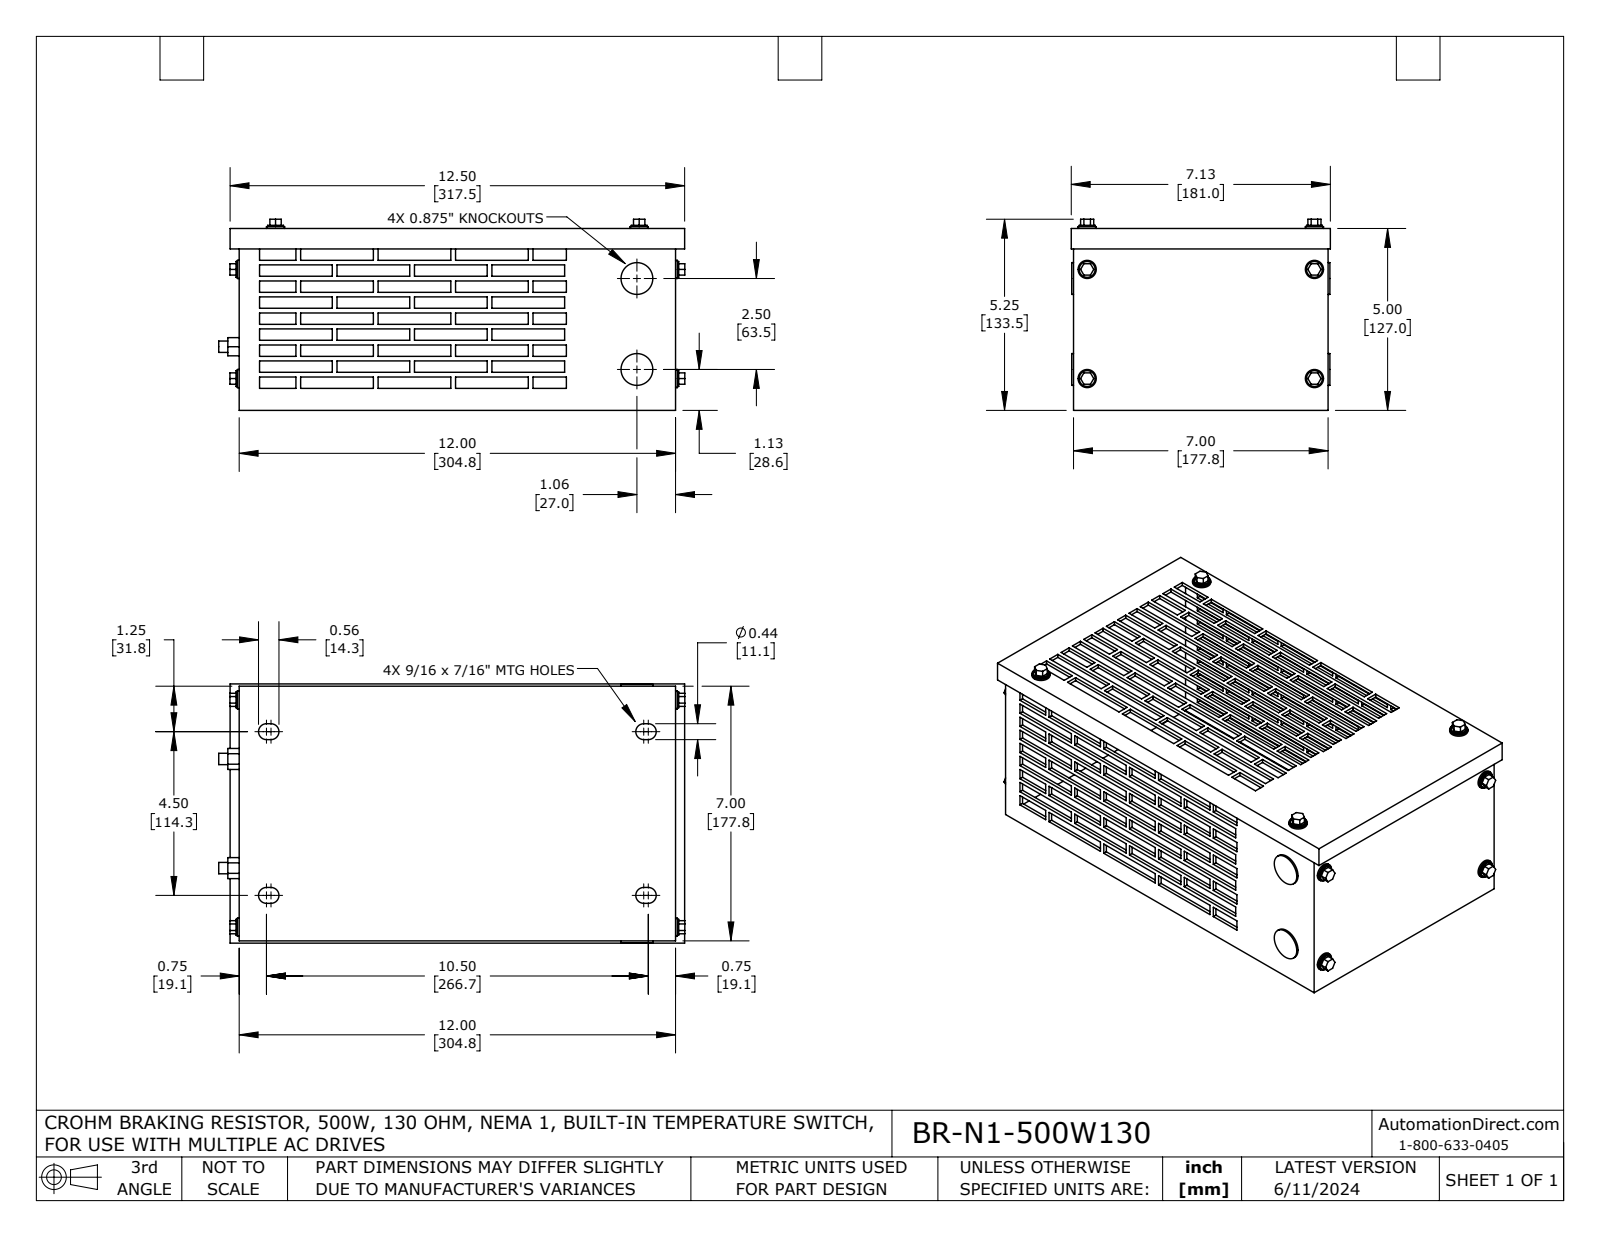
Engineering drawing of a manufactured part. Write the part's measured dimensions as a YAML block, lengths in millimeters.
part_name: "BR-N1-500W130"
step_written_by: "SolidWorks 2021 (AUTOMOTIVE_DESIGN)"
units: millimeters
bodies: {solids: 31, faces: 846, planar: 746, cylindrical: 100, other: 0}
overall_size: [325.6, 181, 133.5]
volume: 468500
surface_area: 412400
round_holes:
  - {diameter: 6.4, count: 8}
  - {diameter: 19.1, count: 2}
round_bosses_or_shafts:
  - {diameter: 12.7, count: 8}
  - {diameter: 11.1, count: 8}
  - {diameter: 22.2, count: 2}
  - {diameter: 8, count: 2}
partial_cylinders:
  - {radius: 5.6, count: 8}
face_to_face_distances: [2.5, 124.5, 302.3, 175.3, 127, 121.9, 304.8, 177.8, 299.7, 172.7]
hole_center_spacings: [158.8, 76.2, 176.1, 254, 299.5, 63.5]
